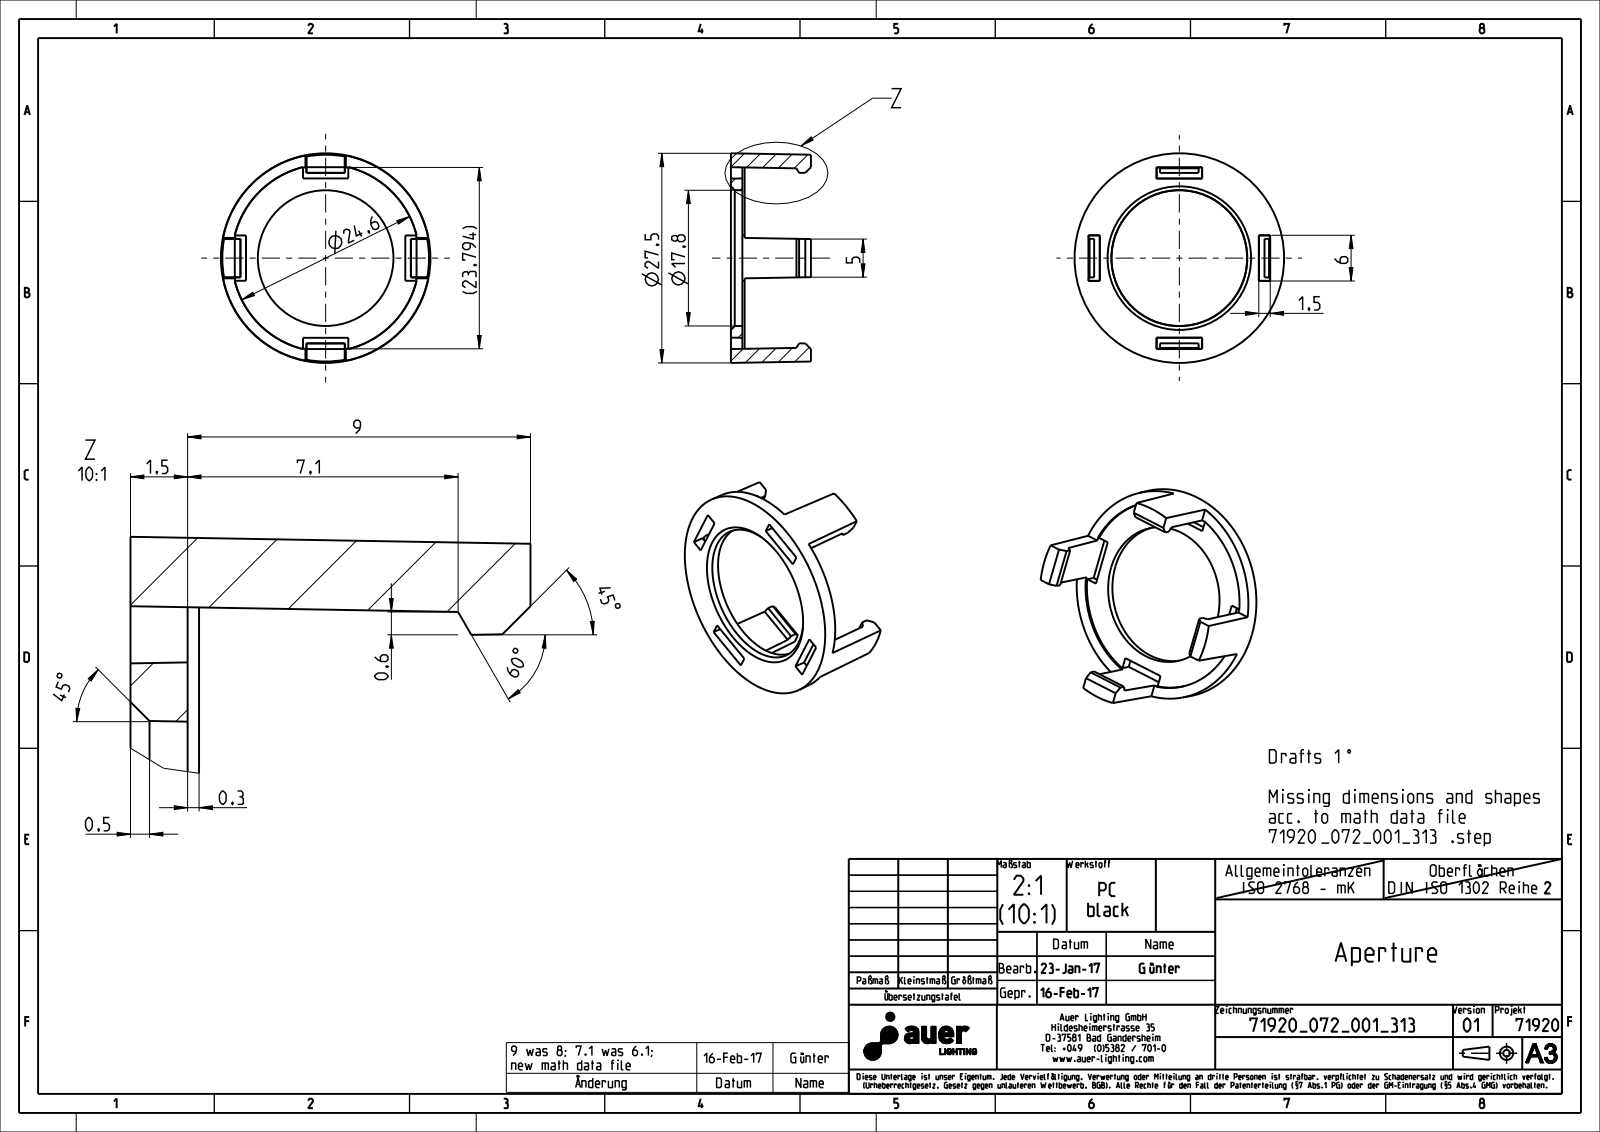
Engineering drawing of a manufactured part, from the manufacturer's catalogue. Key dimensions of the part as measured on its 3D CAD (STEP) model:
Part name (STEP PRODUCT): 71920_072_313
STEP written by: PRO/ENGINEER BY PARAMETRIC TECHNOLOGY CORPORATION, 2010330 (CONFIG_CONTROL_DESIGN)
Units: millimetres
Bodies: 1 solid, 64 faces (54 planar, 0 cylindrical, 10 other)
Overall size (bounding box): 27.5 × 27.5 × 10.5
Volume: 818 mm³ · Surface area: 1 434 mm²
Main face-to-face distances: 1.5, 9.25, 1.8, 22.35, 13.1, 10.5, 9, 8.7, 8.93, 0.32
